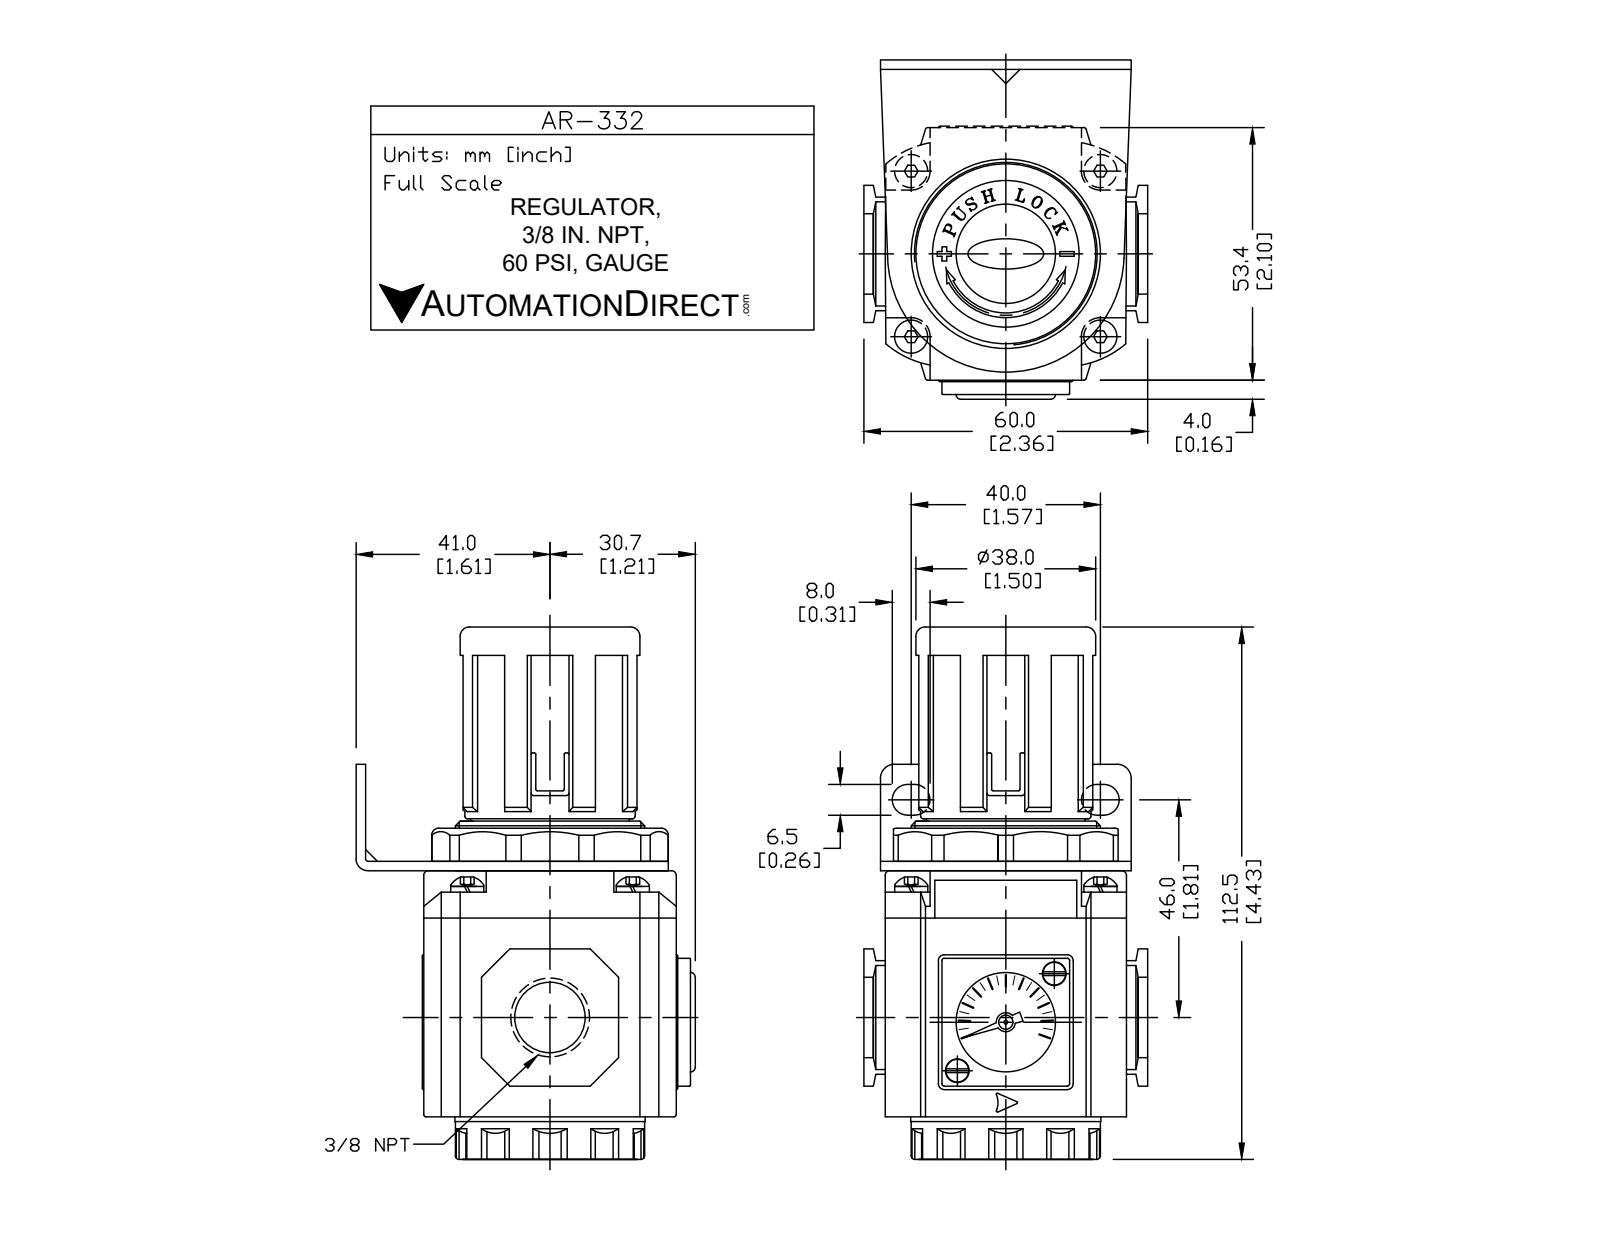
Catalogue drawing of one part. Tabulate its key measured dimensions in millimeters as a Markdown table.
| quantity | value |
| --- | --- |
| part name | AR-332 |
| STEP written by | SolidWorks 2015 (CONFIG_CONTROL_DESIGN) |
| units | millimeters |
| bodies | 14 solids, 501 faces (326 planar, 133 cylindrical, 42 other) |
| overall size | 112.5 × 70.7 × 60 |
| volume | 207 683 mm³ |
| surface area | 44 006 mm² |
| round holes (diameter × count) | 3 × 6, 2 × 1, 14.27 × 1, 21 × 1, 30 × 1, 32 × 1 |
| round bosses / shafts (diameter × count) | 5.5 × 4, 2.7 × 2, 40 × 1, 39.2 × 1, 38 × 1, 33.5 × 1, 20.46 × 1, 4 × 1 |
| partial cylindrical surfaces (radius × count) | 1 × 12, 1.2 × 10, 3.25 × 6, 4 × 5, 0.3 × 4, 19.9 × 4, 0.2 × 3, 2 × 1 |
| main face-to-face distances | 2, 52, 54, 53.4, 1, 9, 61, 51, 55.5, 52.4 |
| hole center spacings | 26.58, 14.5, 35, 40, 53.15, 28.99 |
